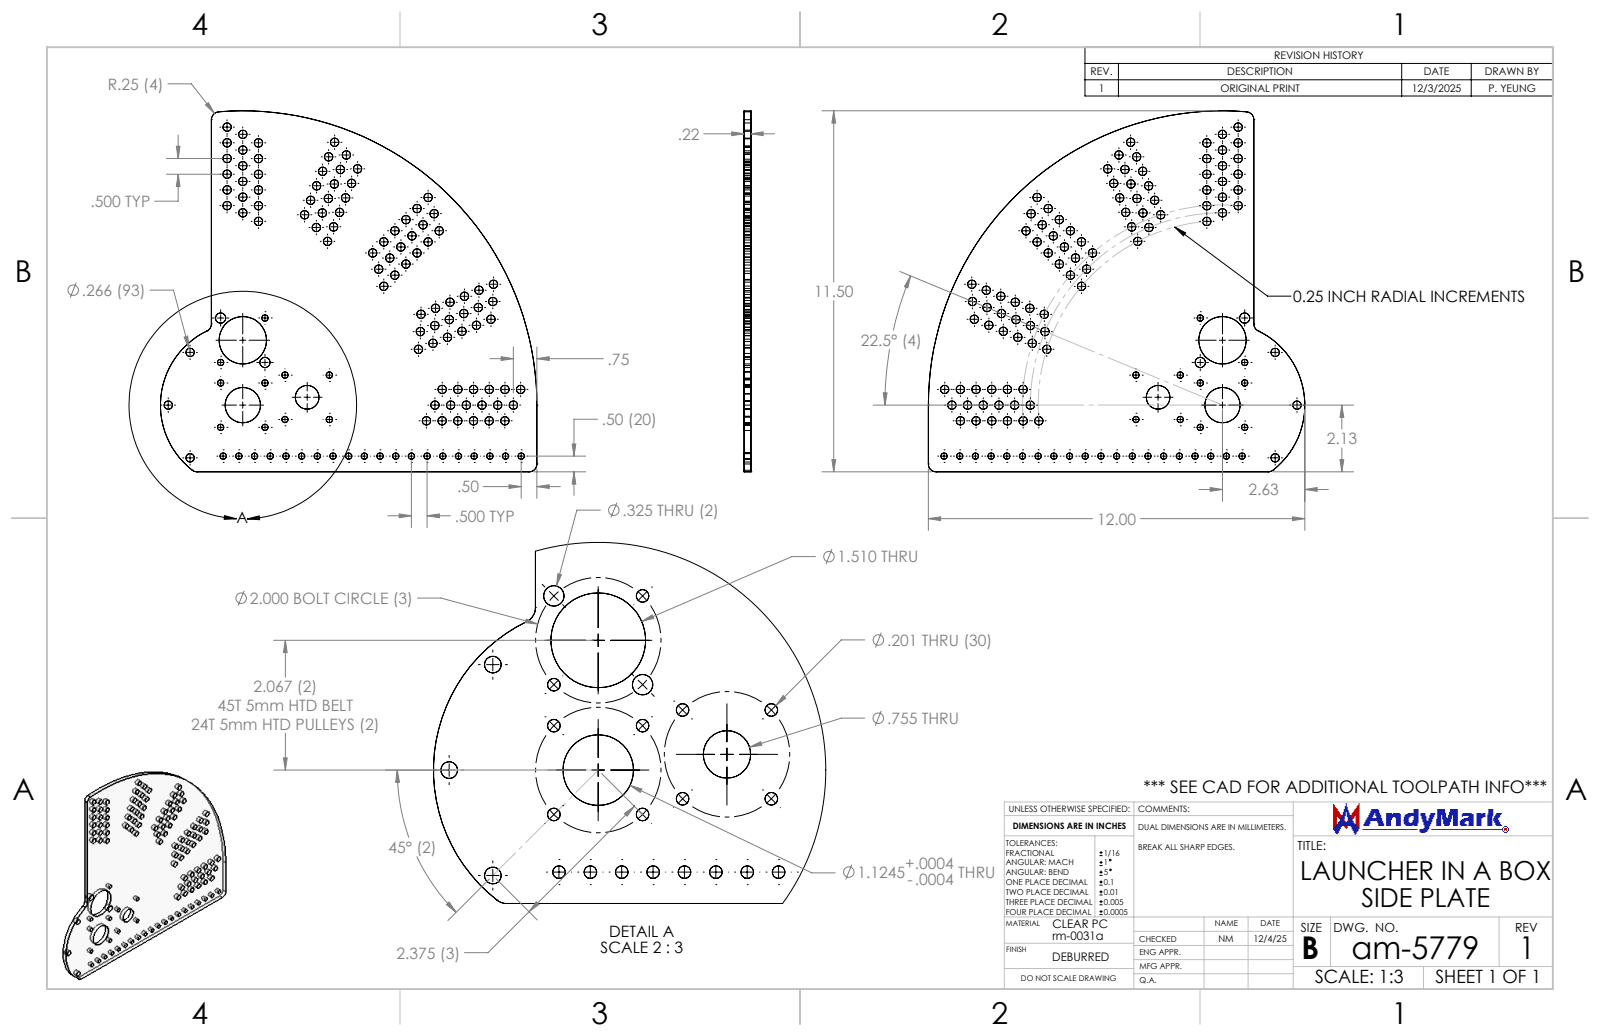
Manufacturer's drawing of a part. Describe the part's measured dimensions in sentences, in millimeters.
The part is named "am-5779 Launcher in a Box Side Plate". Its 3-D file was written by "SolidWorks 2024 (AUTOMOTIVE_DESIGN)". It is 1 solid with 268 faces: 5 planar, 263 cylindrical and 0 other. Overall it measures 304.8 by 292.1 by 5.6 millimeters. Its volume is 347 900 cubic millimeters and its surface area 145 900 square millimeters. Round holes: 93 of diameter 6.8, 30 of diameter 5.1, 2 of diameter 8.3, 1 of diameter 19.2, 1 of diameter 28.5, 1 of diameter 38.4. Partial cylindrical surfaces (rounded edges, fillets, slot ends): 4 of radius 6.4, 1 of radius 66.7, 1 of radius 238.1. The main face-to-face distances are 5.6, 263.5. The hole center spacings are 25.4, 50.8, 12.7, 35.9, 38.1, 63.5, 76.2, 52.5.
